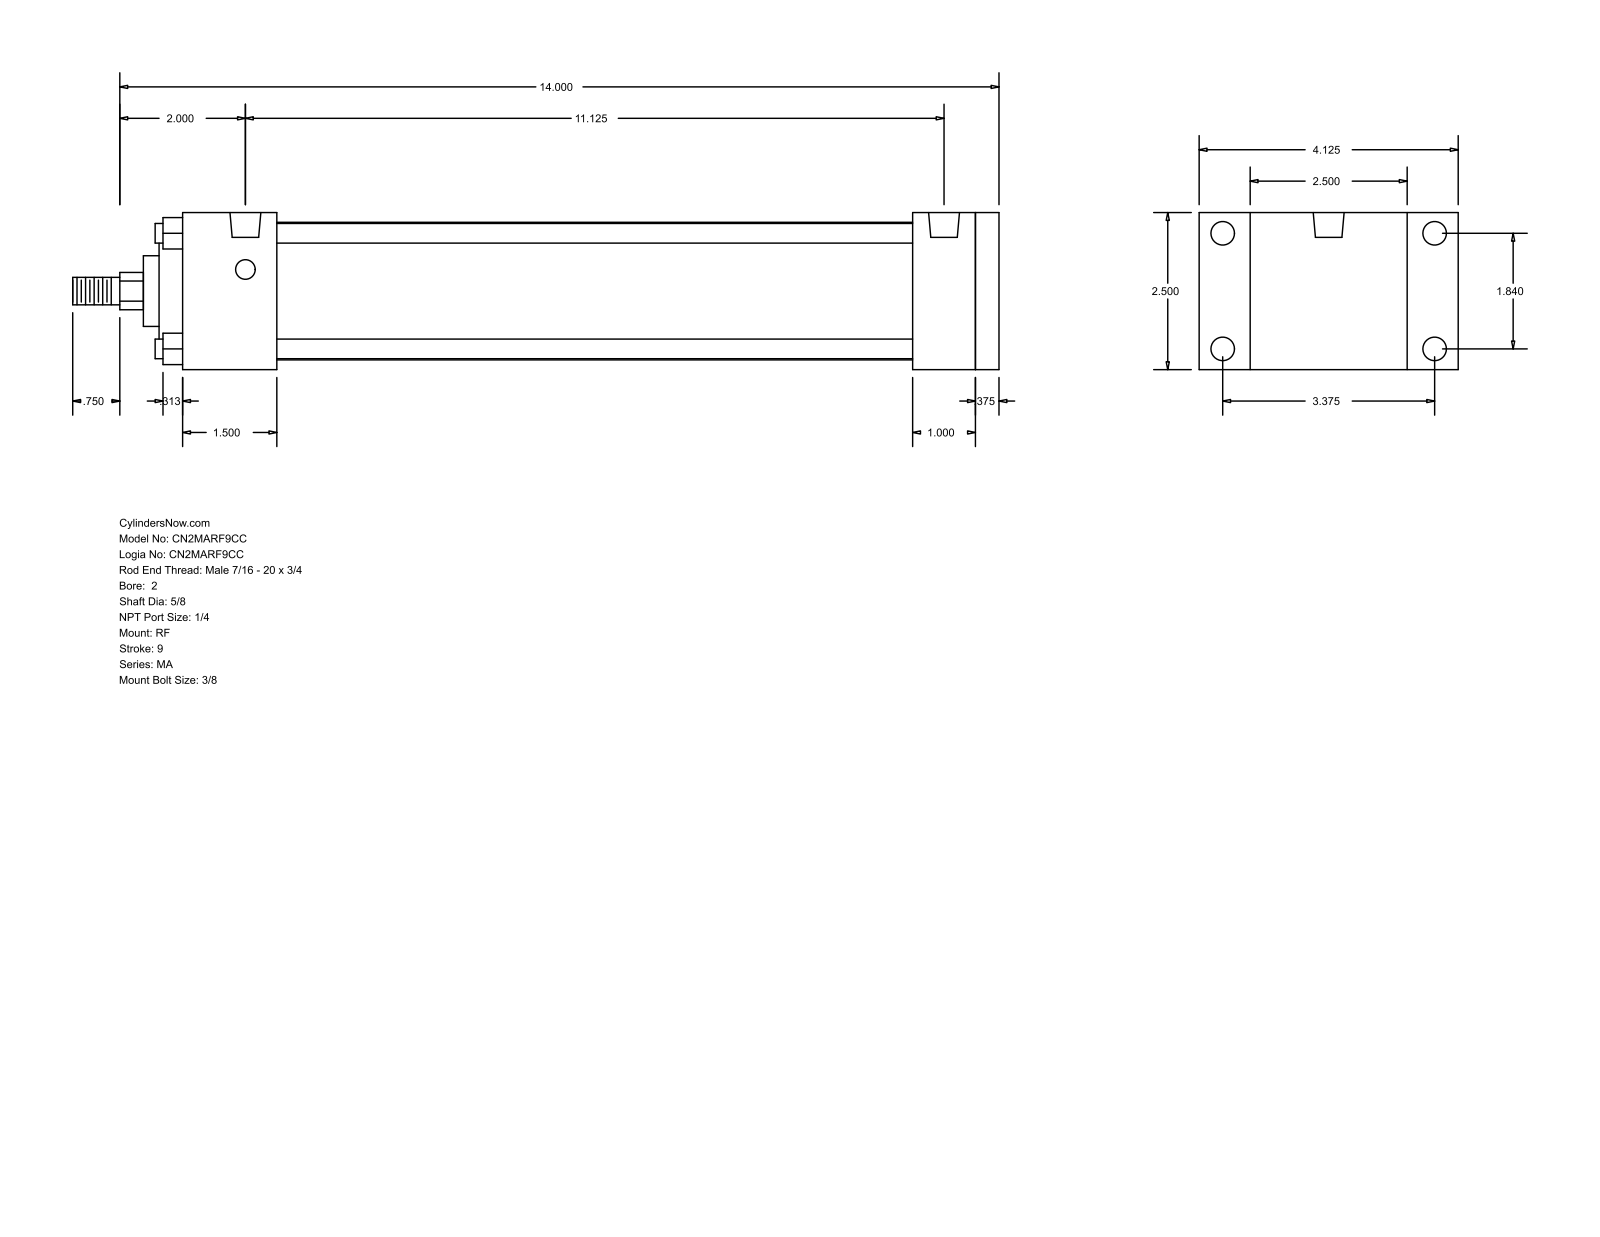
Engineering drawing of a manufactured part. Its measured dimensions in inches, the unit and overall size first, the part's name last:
Units: inches
Overall size (bounding box): 14.75 × 4.125 × 2.5
Round holes (diameter × count): ⌀0.313 ×4, ⌀0.375 ×4, ⌀0.492 ×2
Round bosses / shafts (diameter × count): ⌀0.313 ×4, ⌀2.19 ×1, ⌀2 ×1, ⌀1.125 ×1, ⌀0.625 ×1, ⌀0.437 ×1
Partial cylindrical surfaces — rounded edges, fillets, slot ends (radius × count): R0.297 ×1
Main face-to-face distances: 2.5, 0.375, 1.5, 12.625, 13, 13.375, 11.125, 11.5, 11.625, 10.125
Hole centre spacings: 1.84, 3.375, 3.844, 11.125
Bodies: 0 solids, 94 faces (65 planar, 29 cylindrical, 0 other)
Part name (STEP PRODUCT): MA_RF__0200_0.625
STEP written by: GSSL Pune (CONFIG_CONTROL_DESIGN)
